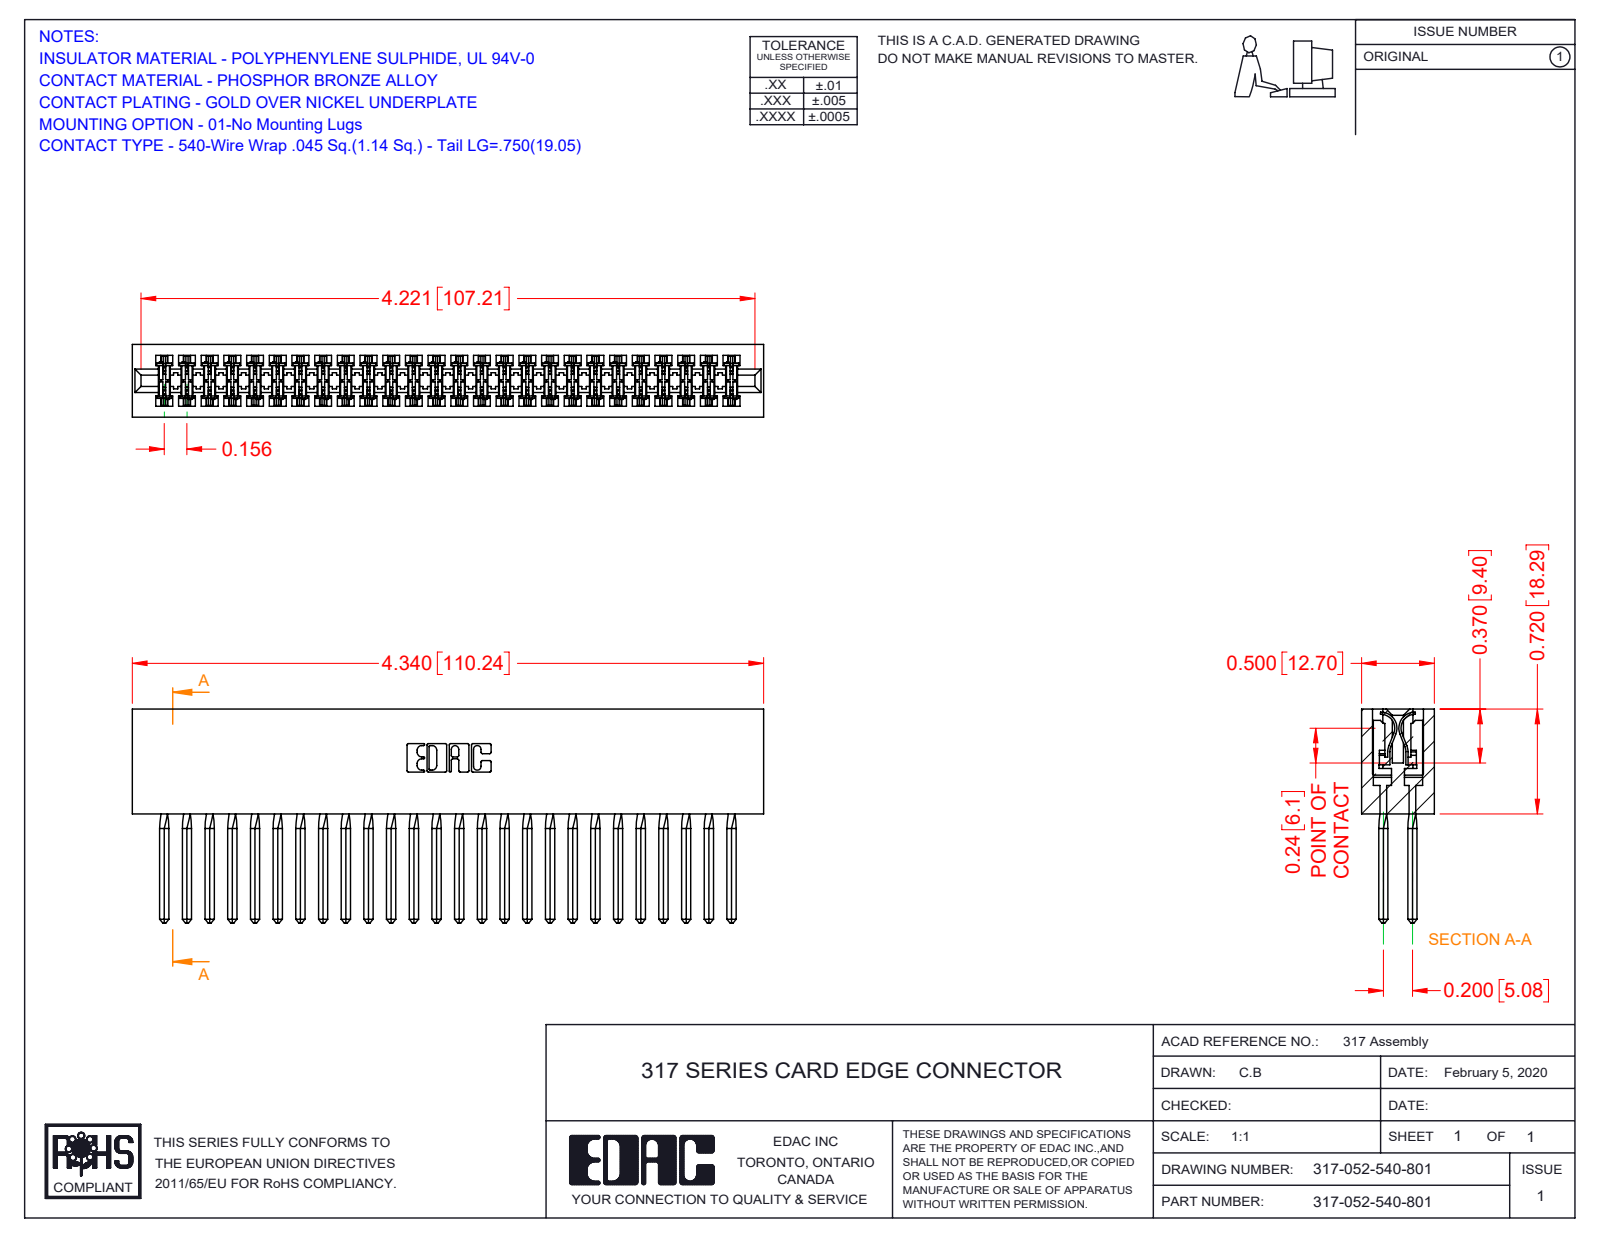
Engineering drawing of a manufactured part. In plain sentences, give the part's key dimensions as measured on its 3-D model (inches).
The part is named "317-290-001_540; 317-052-540-801; 317 Part_Lugless". Its 3-D file was written by "SolidWorks 2016 (CONFIG_CONTROL_DESIGN)". It is 53 solids with 4718 faces: 3846 planar, 664 cylindrical and 208 other. Overall it measures 4.34 by 1.47 by 0.5 inches. Its volume is 1.205 cubic inches and its surface area 45.11 square inches. Partial cylindrical surfaces (rounded edges, fillets, slot ends): 104 of radius 0.015, 22 of radius 0.01, 6 of radius 0.007, 6 of radius 0.031, 3 of radius 0.026, 2 of radius 0.095, 2 of radius 0.1, 2 of radius 0.11. The main face-to-face distances are 0.075, 0.5, 0.425, 0.35, 0.11, 0.195, 0.094, 0.72, 0.2, 0.115.
